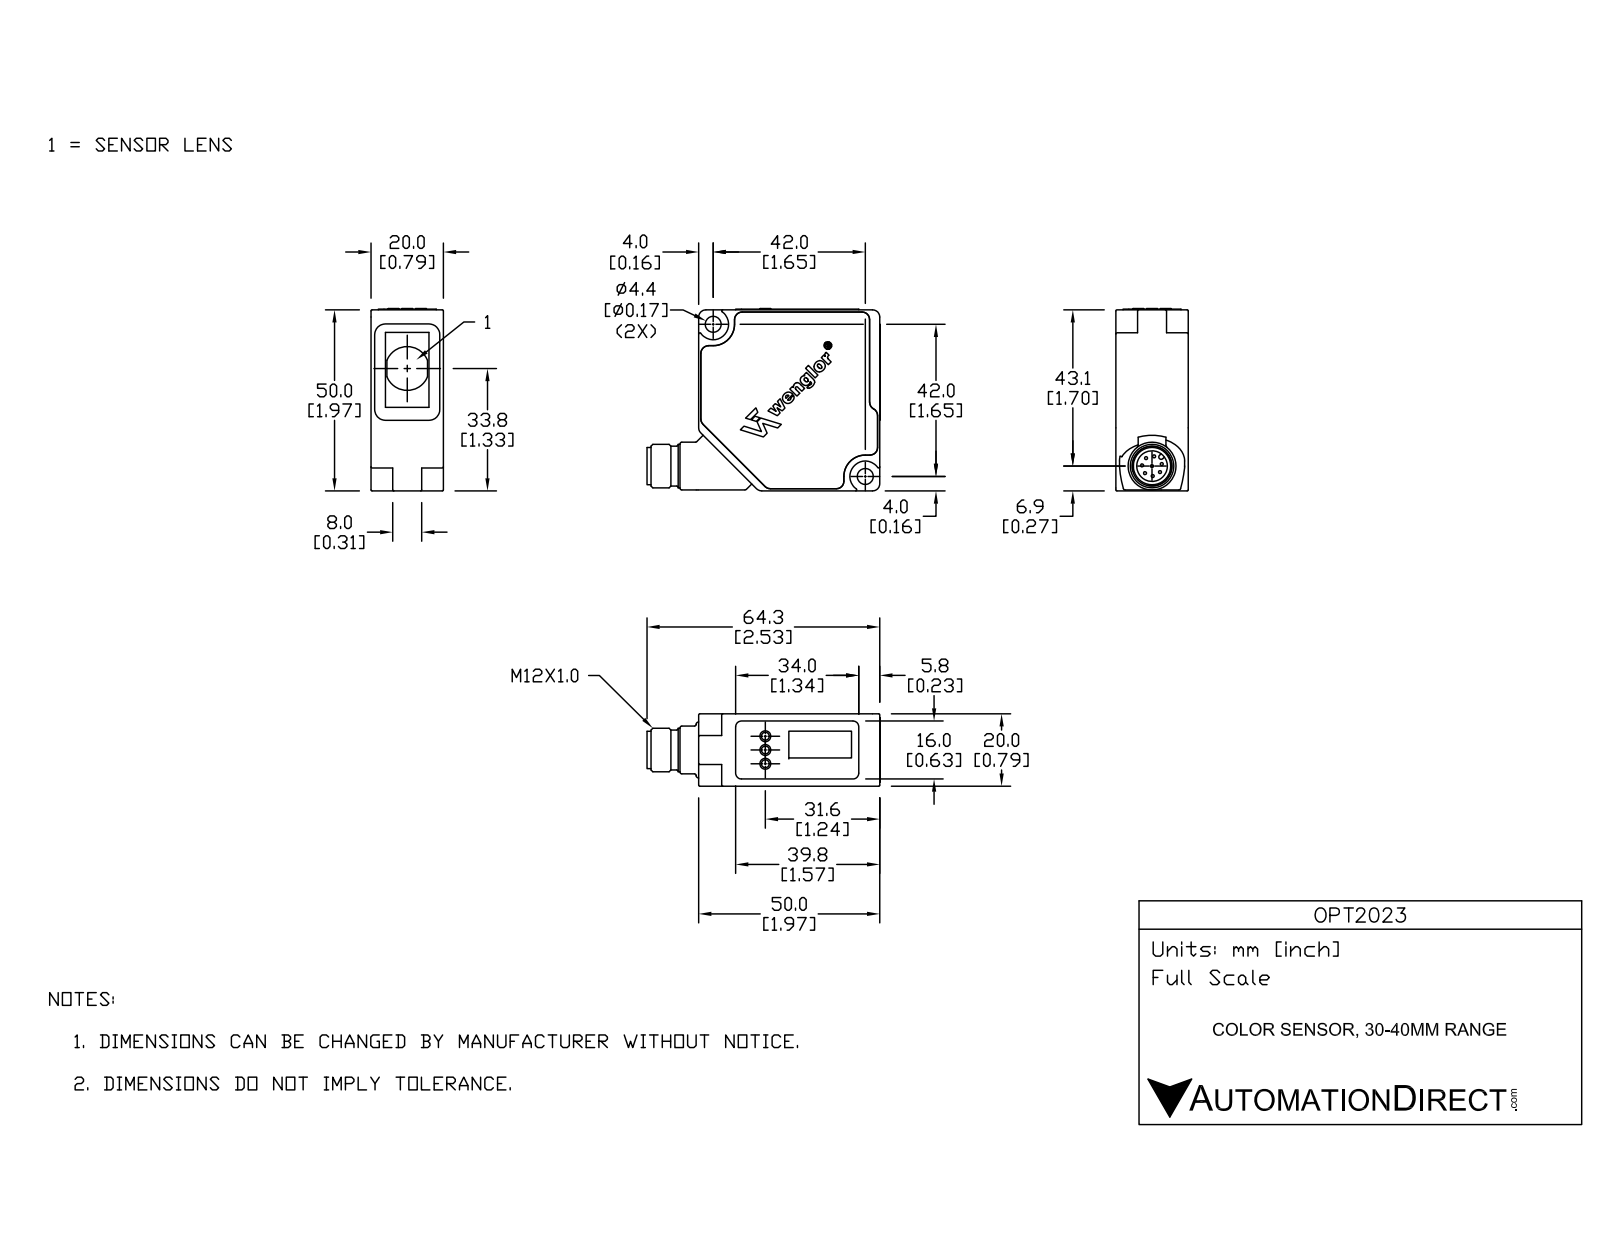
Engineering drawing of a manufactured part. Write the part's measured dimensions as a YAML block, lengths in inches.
part_name: "OFP401P0189; 1018114"
step_written_by: "Unknown (AUTOMOTIVE_DESIGN)"
units: inches
bodies: {solids: 2, faces: 758, planar: 319, cylindrical: 236, other: 203}
overall_size: [2.537, 1.982, 0.787]
volume: 5.465
surface_area: 29.79
round_holes:
  - {diameter: 0.173, count: 2}
  - {diameter: 0.333, count: 1}
round_bosses_or_shafts:
  - {diameter: 0.032, count: 8}
  - {diameter: 0.118, count: 3}
  - {diameter: 0.055, count: 3}
  - {diameter: 0.185, count: 2}
  - {diameter: 0.709, count: 1}
  - {diameter: 0.52, count: 1}
  - {diameter: 0.472, count: 1}
  - {diameter: 0.433, count: 1}
partial_cylinders:
  - {radius: 0.012, count: 28}
  - {radius: 0.024, count: 10}
  - {radius: 0.079, count: 10}
  - {radius: 0.004, count: 8}
  - {radius: 0.008, count: 8}
  - {radius: 0.059, count: 6}
  - {radius: 0.02, count: 5}
  - {radius: 0.037, count: 5}
face_to_face_distances: [0.776, 0.787, 0.764, 1.961, 1.969, 0.039, 1.932, 0.044, 1.976, 1.953]
hole_center_spacings: [2.339]
